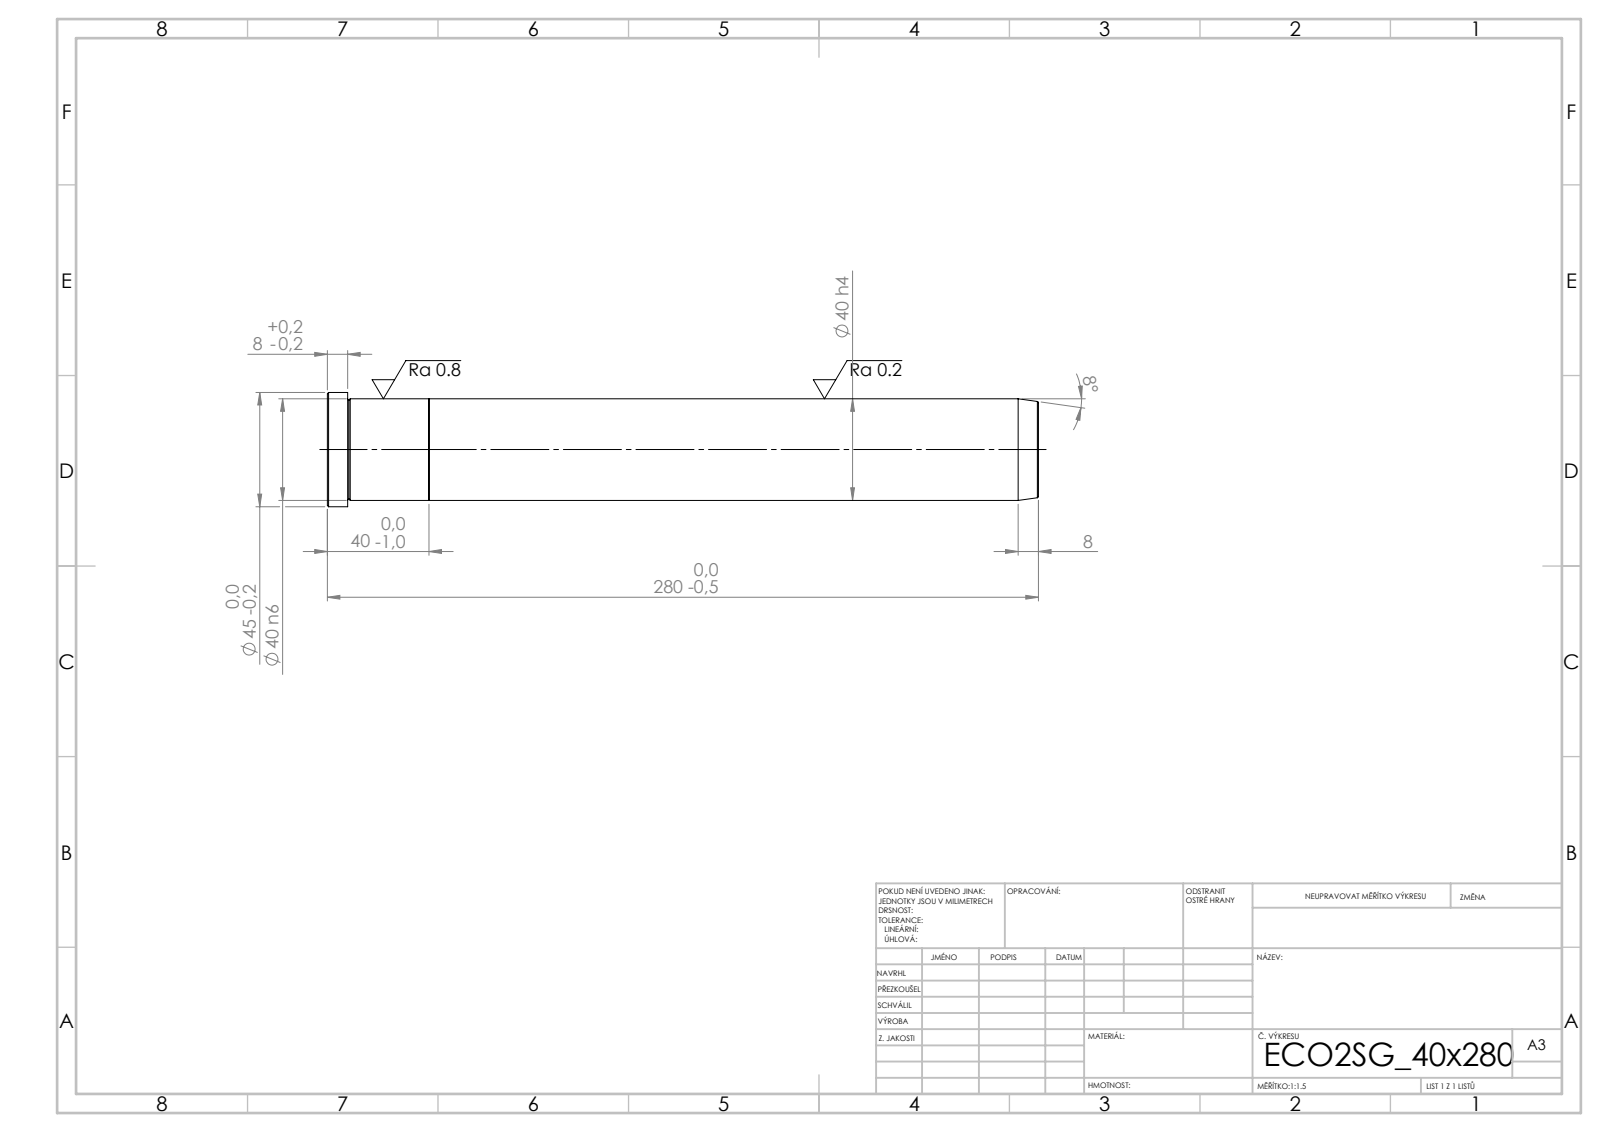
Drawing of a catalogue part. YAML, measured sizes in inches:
step_written_by: "SolidWorks 2019 (CONFIG_CONTROL_DESIGN)"
units: inches
bodies: {solids: 2, faces: 21, planar: 5, cylindrical: 6, other: 10}
overall_size: [11.024, 1.772, 1.772]
volume: 21.6
surface_area: 63.33
round_bosses_or_shafts:
  - {diameter: 1.772, count: 1}
  - {diameter: 1.575, count: 1}
face_to_face_distances: [1.575, 9.449, 11.024, 10.709, 1.26, 0.315]
